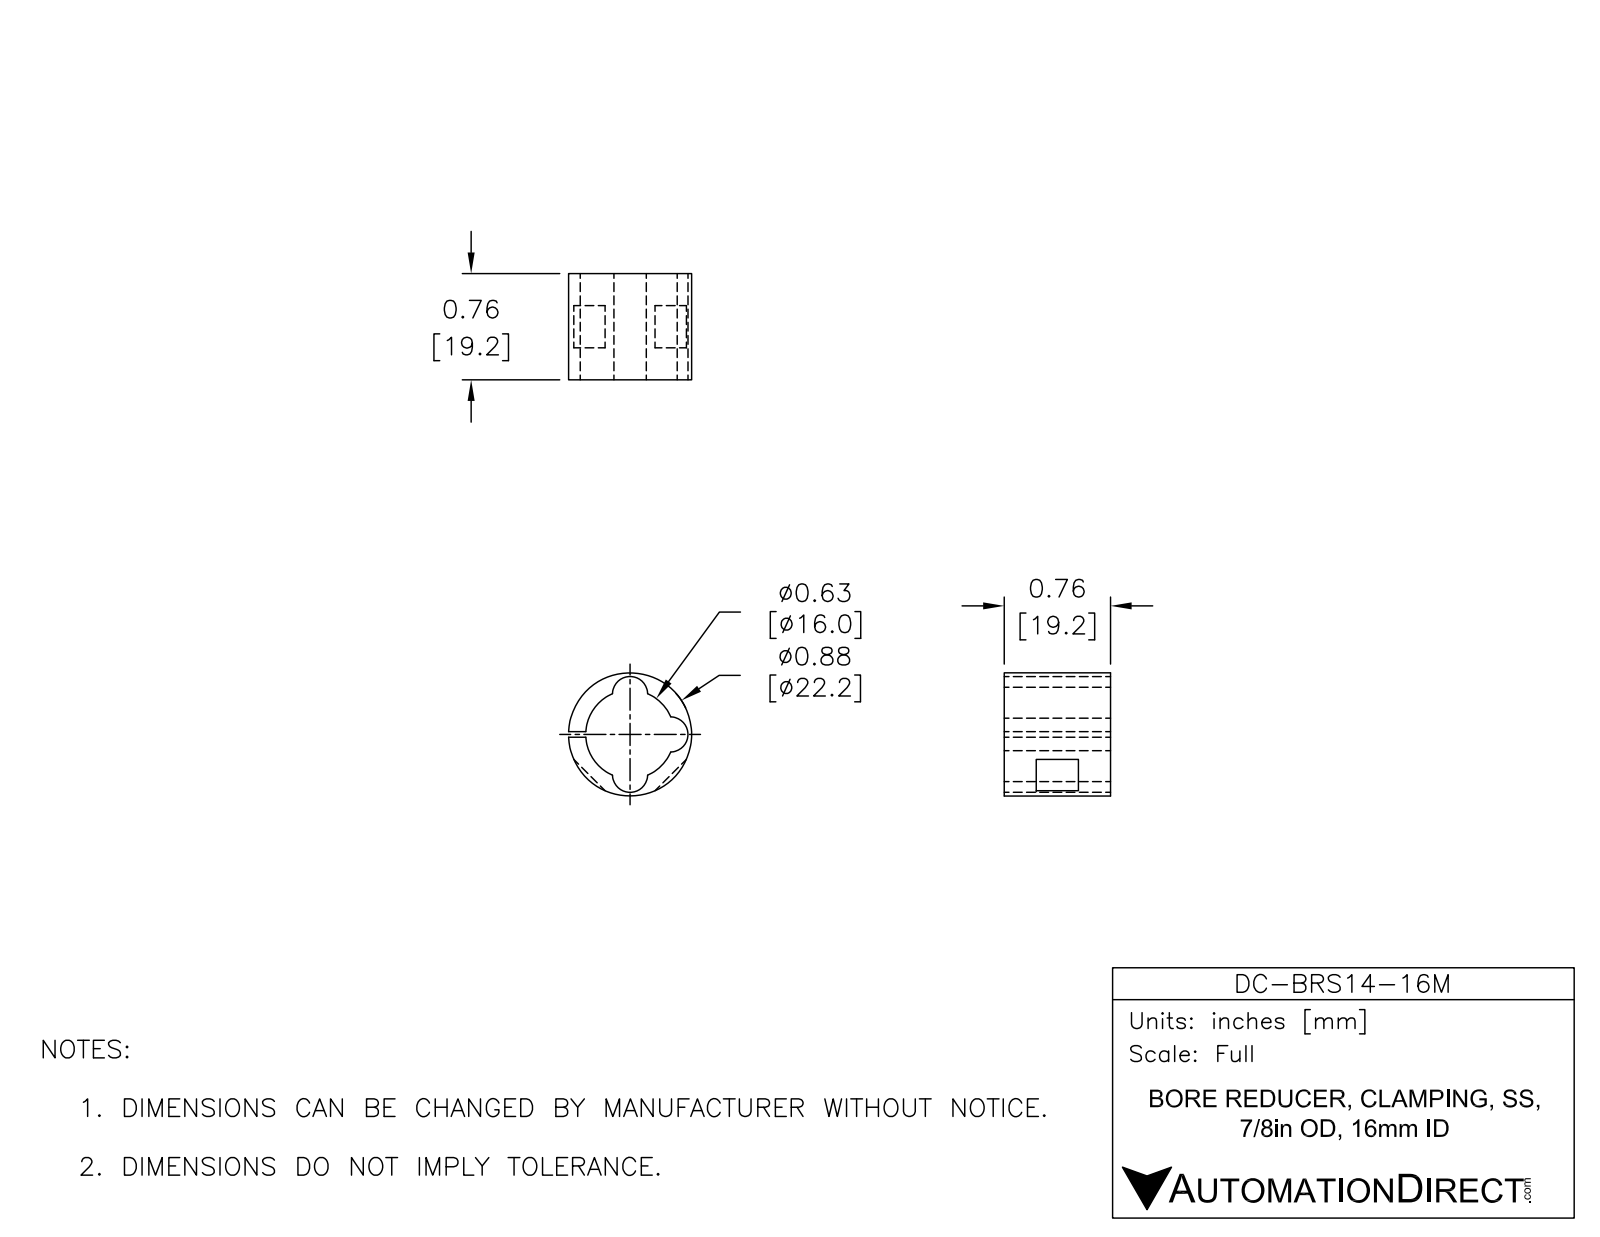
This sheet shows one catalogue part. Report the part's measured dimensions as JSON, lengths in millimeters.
{"part_name": "DC-BRS14-16M", "step_written_by": "SolidWorks 2015 (AUTOMOTIVE_DESIGN)", "units": "millimeters", "bodies": {"solids": 1, "faces": 20, "planar": 10, "cylindrical": 10, "other": 0}, "overall_size": [22.23, 22.21, 19.18], "volume_mm3": 2738, "surface_area_mm2": 2879, "round_bosses_or_shafts": [[22.22, 1]], "partial_cylinders_radius": [[3.17, 3], [8, 1]], "face_to_face_distances": [19.18, 1.02, 5.78, 13.4, 7.62]}
